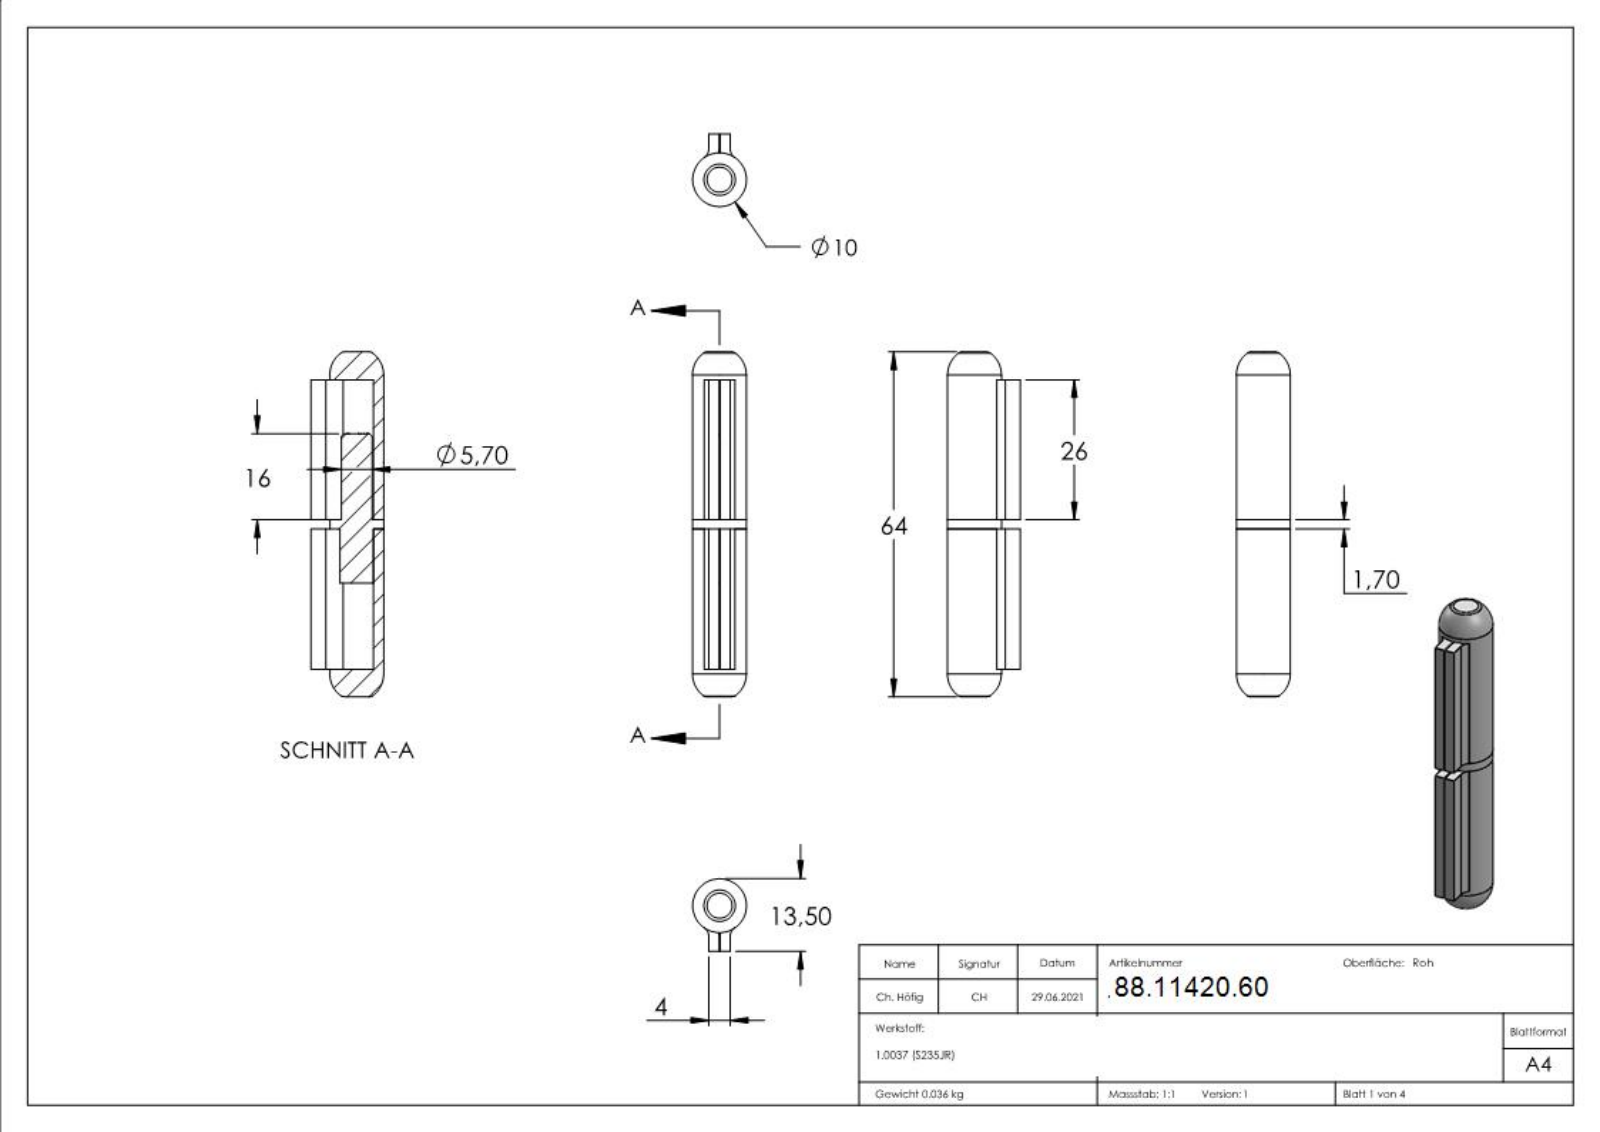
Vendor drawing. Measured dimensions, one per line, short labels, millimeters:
name: 420-XX Teil1; 420-XX Teil1_420-60 Teil1; 420-XX Teil2; 420-XX Teil2_420-60 Teil2 (+1 more)
written by: SolidWorks 2018 (CONFIG_CONTROL_DESIGN)
unit: mm
bodies: 3 solids, 283 faces (150 planar, 22 cylindrical, 111 other)
size: 64 × 13.5 × 10
volume: 4 622 mm³; area: 4 767 mm²
holes: 1× ⌀6.2
bosses: 1× ⌀10, 1× ⌀5.7
rounds: 2× R2, 2× R3.9
face distances: 1.9, 2.1, 4, 27.7, 1.7, 26, 53.7, 16, 10, 5.15
